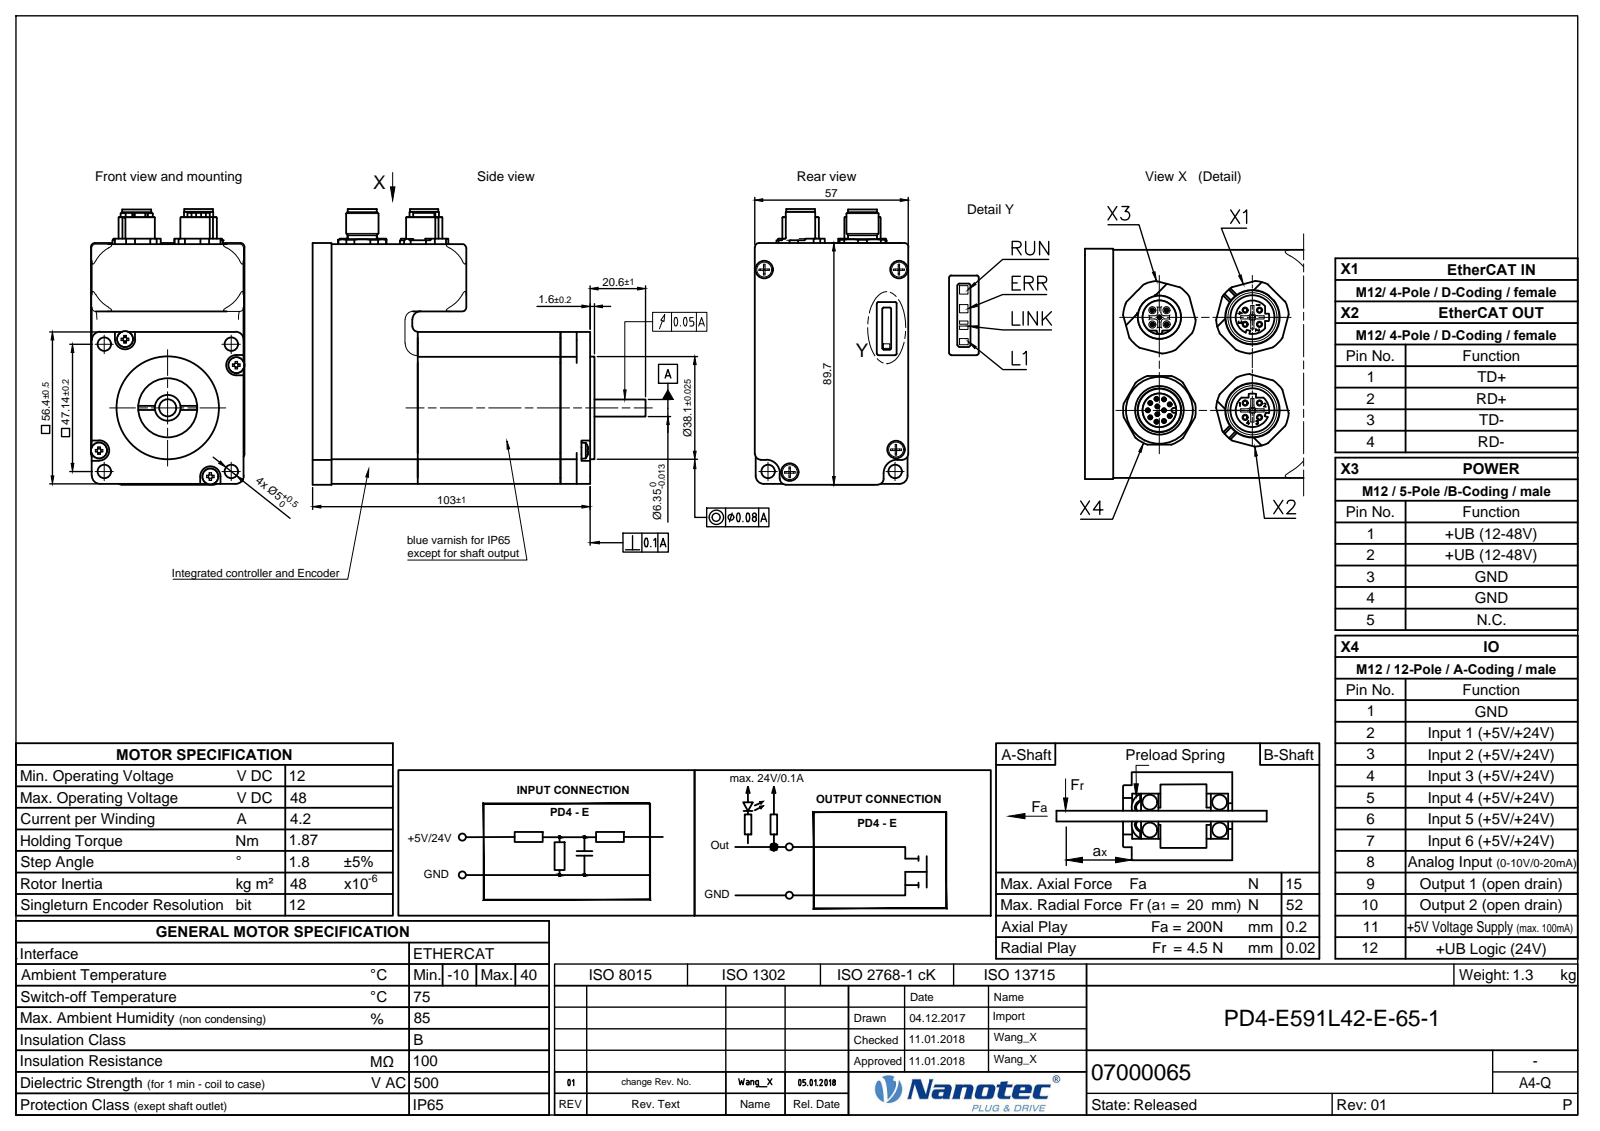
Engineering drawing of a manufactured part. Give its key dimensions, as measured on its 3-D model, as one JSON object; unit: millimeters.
{"part_name": "PD4-E591L42-E-65-1", "step_written_by": "Autodesk Inventor 2017 (AUTOMOTIVE_DESIGN)", "units": "millimeters", "bodies": {"solids": 17, "faces": 1538, "planar": 784, "cylindrical": 471, "other": 283}, "overall_size": [123.6, 102.3, 57], "volume_mm3": 251922, "surface_area_mm2": 86625, "round_holes": [[1.2, 12], [1.1, 10], [2.5, 6], [1.7, 4], [3.2, 4], [3.4, 4], [5, 4], [15.3, 4], [2, 2], [2.01, 2], [2.46, 2], [10.9, 2]], "round_bosses_or_shafts": [[1.3, 13], [1.1, 12], [0.63, 12], [3, 8], [1, 5], [5.5, 4], [2.75, 4], [2.69, 4]], "partial_cylinders_radius": [[2, 44], [0.2, 20], [0.1, 16], [0.5, 16], [0.3, 15], [0.8, 12], [2.2, 12], [0.15, 10]], "face_to_face_distances": [56.4, 2.5, 92, 3.3, 88.7, 27, 53.9, 64, 30, 12], "hole_center_spacings": [3.54, 2.5, 2.9, 21.3, 23, 24.83, 1.87, 4.83]}
